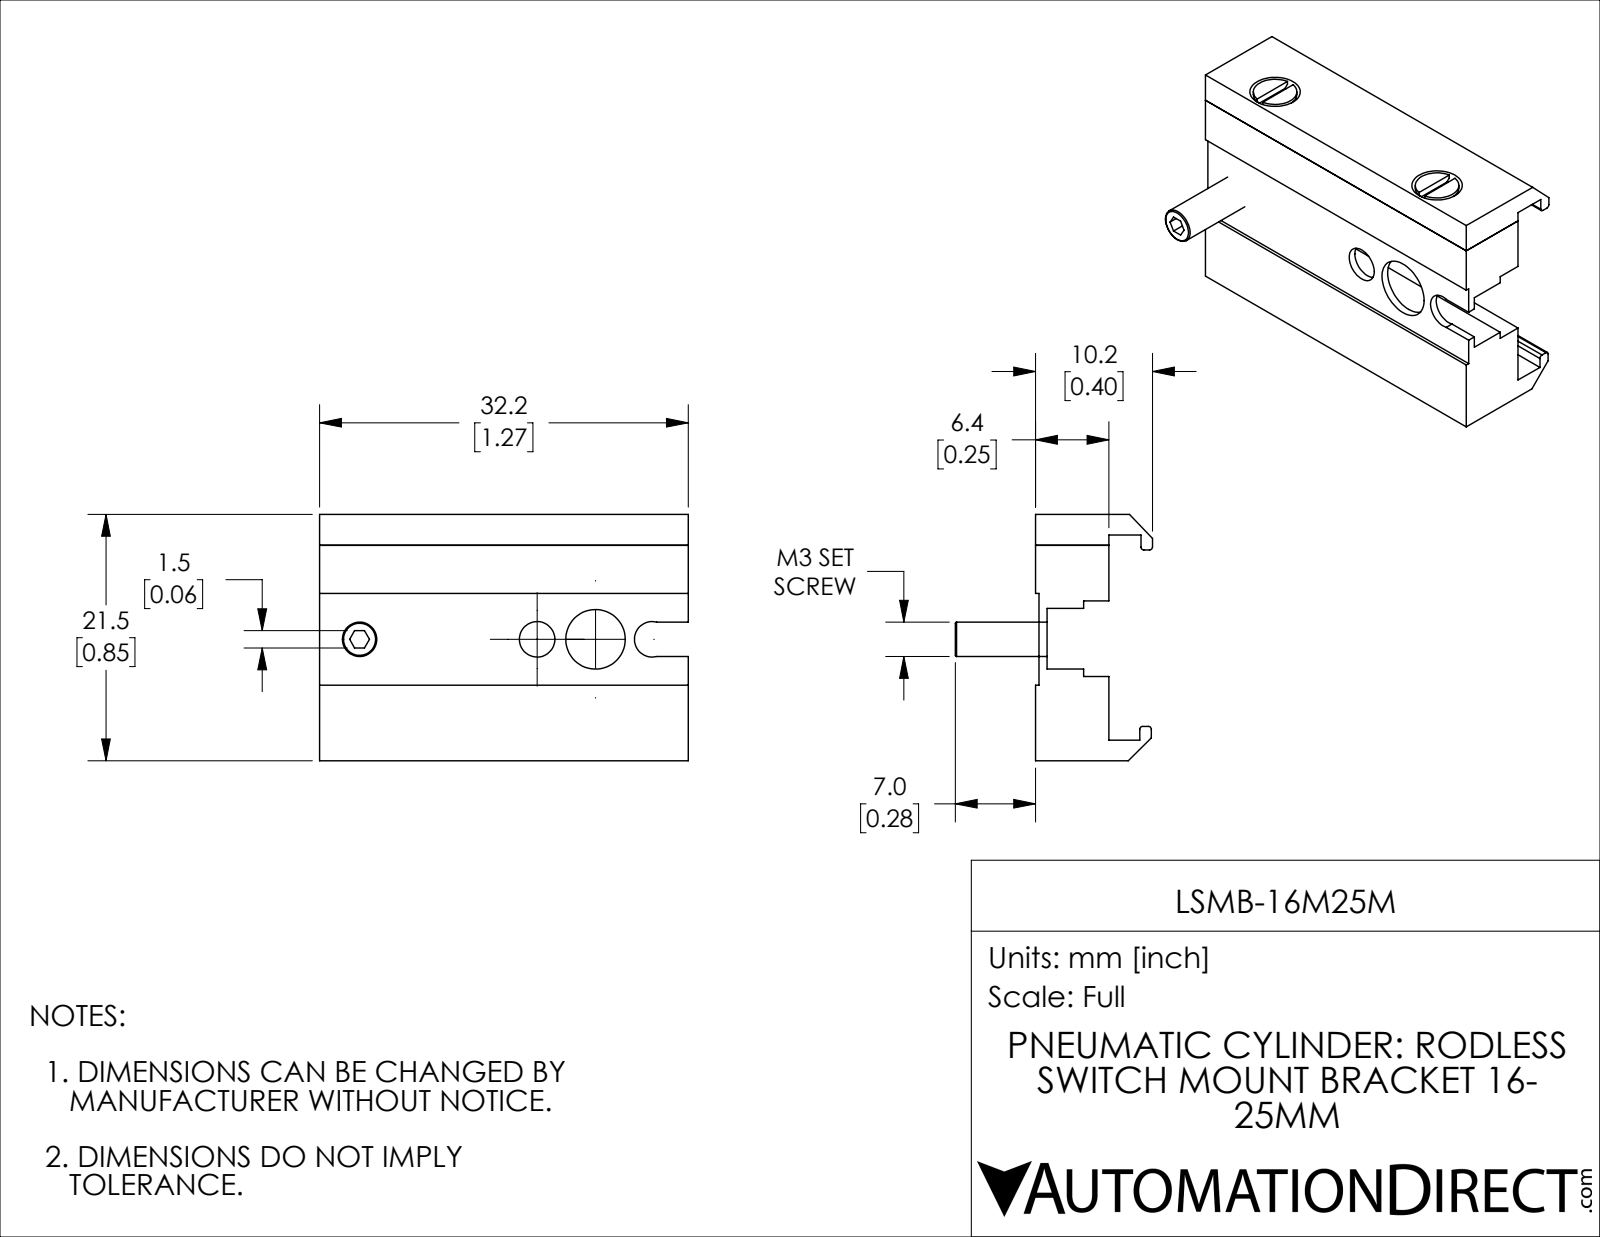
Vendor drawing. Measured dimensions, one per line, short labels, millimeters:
name: LSMB-16M25M
written by: SolidWorks 2019 (CONFIG_CONTROL_DESIGN)
unit: mm
bodies: 5 solids, 103 faces (58 planar, 29 cylindrical, 16 other)
size: 32.2 × 21.5 × 17.2
volume: 3 718 mm³; area: 3 563 mm²
holes: 2× ⌀1.6, 2× ⌀2.4, 1× ⌀2.5, 1× ⌀3.1, 1× ⌀5.2
bosses: 2× ⌀3.8, 2× ⌀2, 1× ⌀3
rounds: 4× R0.25, 1× R1.55
face distances: 6.4, 2.7, 18.8, 21.5, 6.1, 1.8, 19.7, 1, 0.65, 5.95
hole spacings: 5.1, 15.5, 20, 20.6
